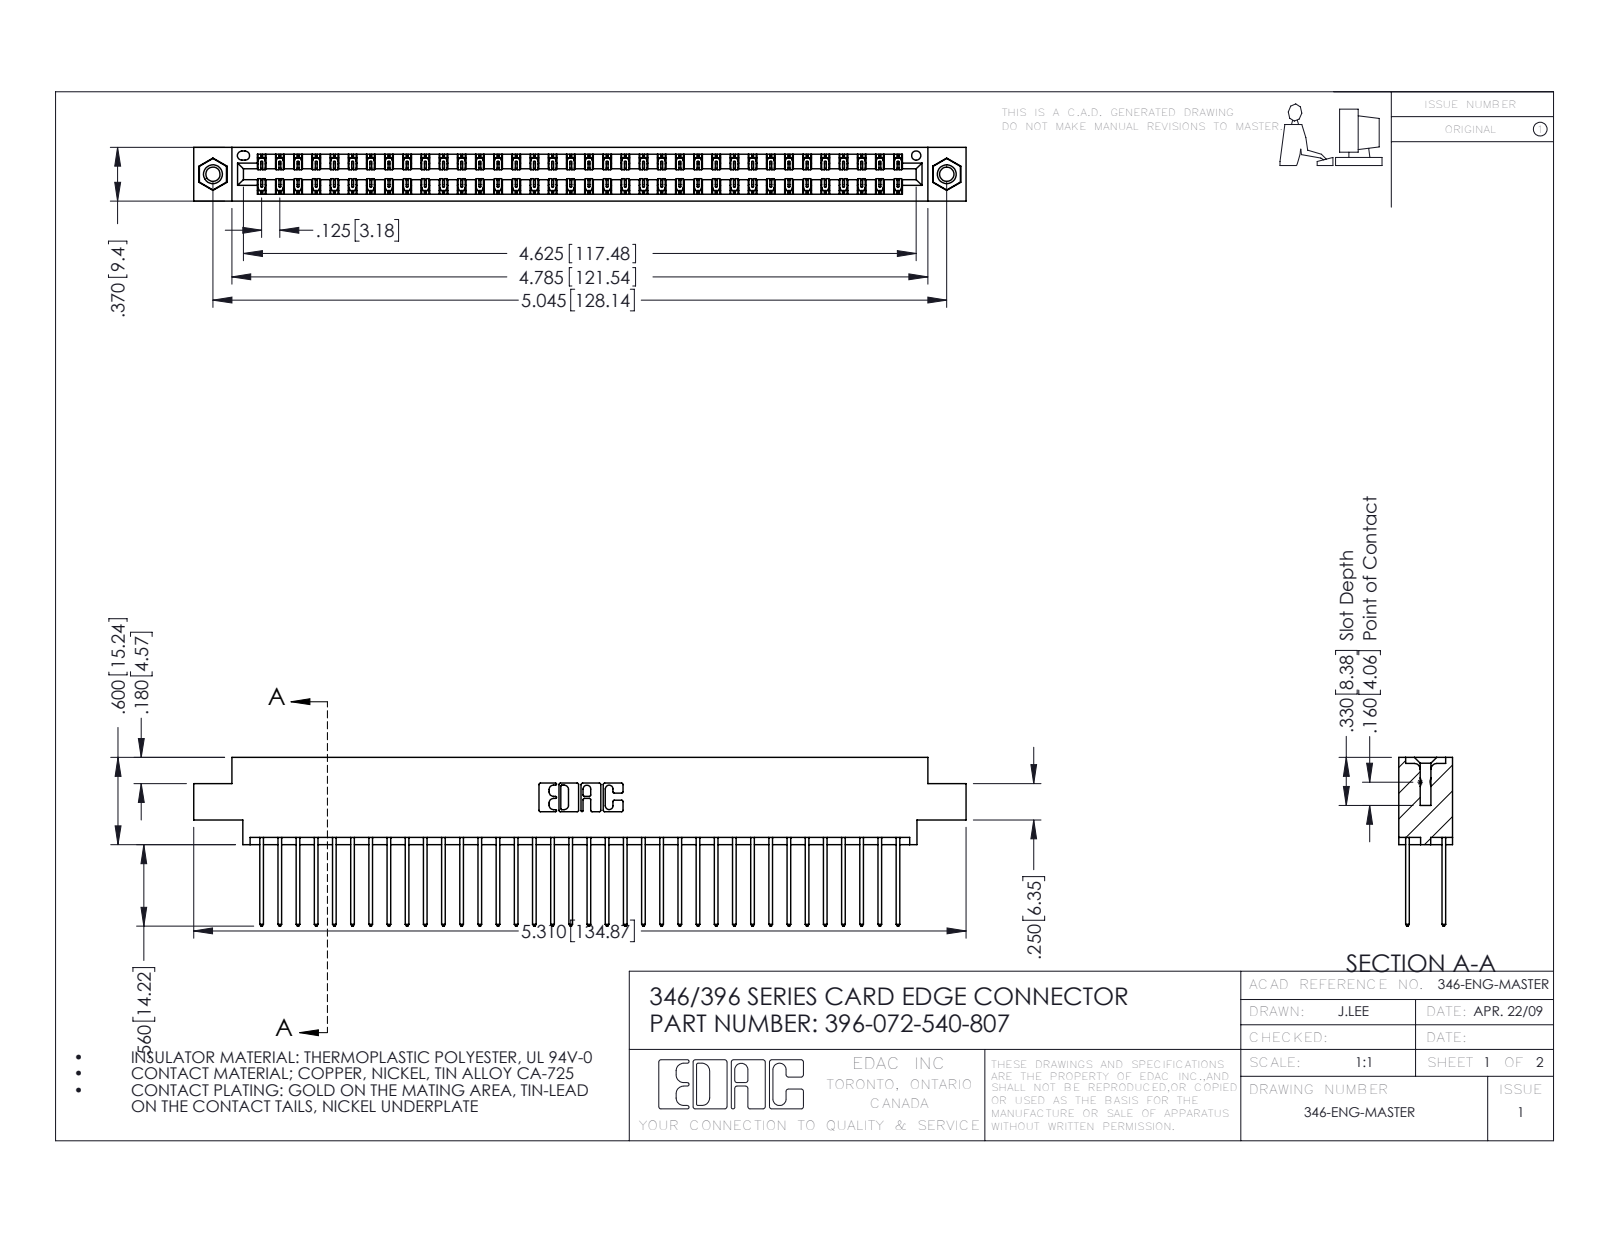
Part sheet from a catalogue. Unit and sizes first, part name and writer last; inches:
Units: inches
Overall size (bounding box): 5.31 × 1.16 × 0.37
Round holes (diameter × count): ⌀0.098 ×2, ⌀0.125 ×2, ⌀0.156 ×2, ⌀0.064 ×1
Round bosses / shafts (diameter × count): ⌀0.155 ×2
Partial cylindrical surfaces — rounded edges, fillets, slot ends (radius × count): R0.006 ×108, R0.01 ×72, R0.01 ×22, R0.007 ×6, R0.031 ×6, R0.026 ×3, R0.014 ×2, R0.022 ×2
Main face-to-face distances: 0.048, 0.322, 0.25, 0.072, 0.298, 0.025, 0.37, 0.275, 0.222, 0.148
Hole centre spacings: 0.246, 4.836, 5.045
Volume: 0.806 in³ · Surface area: 30.33 in²
Bodies: 75 solids, 3930 faces (2632 planar, 1282 cylindrical, 16 other)
Part name (STEP PRODUCT): 345-250-001_345-250-005-103; 346 Part_0.170 Offset - 0.156 Dia-TI; 345-292-001_345-293-140; 396-072-540-807
STEP written by: SolidWorks 2016 (CONFIG_CONTROL_DESIGN)
